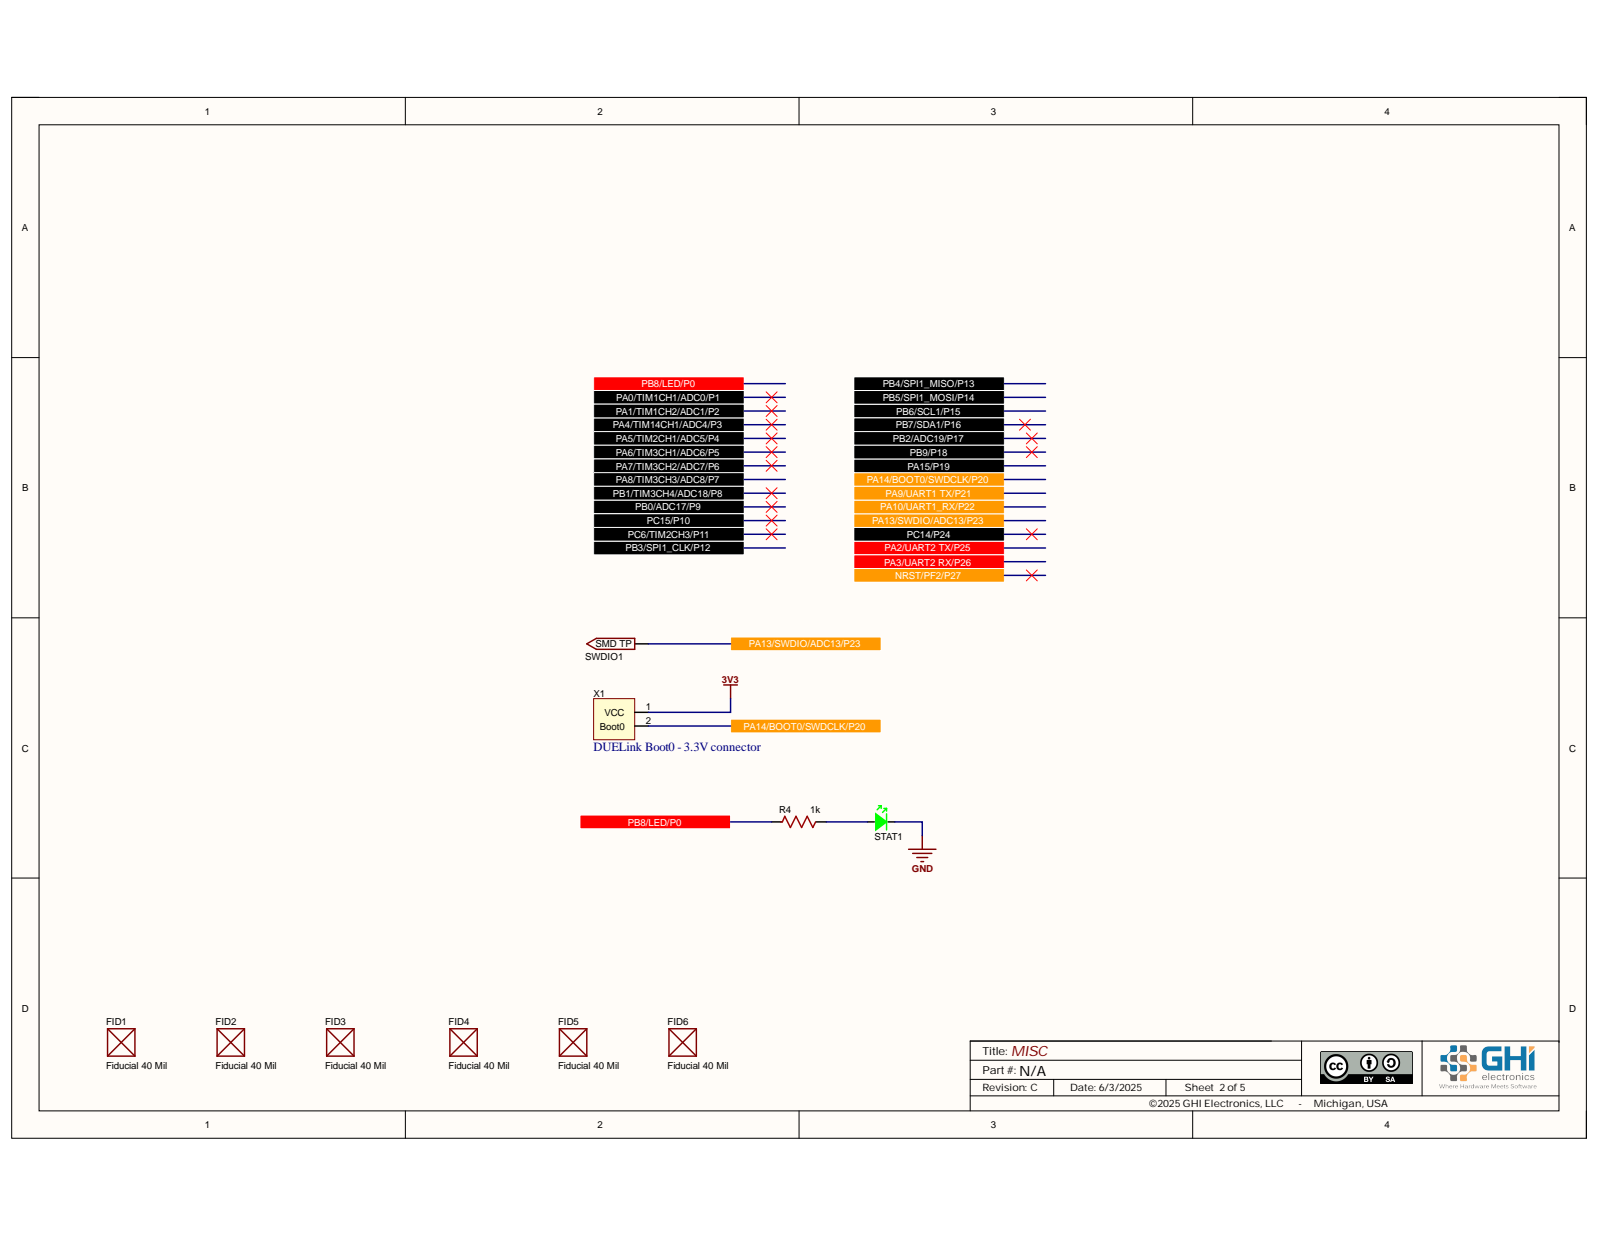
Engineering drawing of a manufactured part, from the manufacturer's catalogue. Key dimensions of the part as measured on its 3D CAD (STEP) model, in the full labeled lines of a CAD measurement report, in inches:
Part name (STEP PRODUCT): PCB; Board; C1; C0402 (+7 more)
STEP written by: Open CASCADE 7.5 (AUTOMOTIVE_DESIGN)
Units: inches
Bodies: 189 solids, 4613 faces (2992 planar, 628 cylindrical, 993 other)
Overall size (bounding box): 1.457 × 1.144 × 0.956
Volume: 0.311 in³ · Surface area: 15.88 in²
Round holes (diameter × count): ⌀0.04 ×12, ⌀0.118 ×4, ⌀0.04 ×2
Partial cylindrical surfaces — rounded edges, fillets, slot ends (radius × count): R0.005 ×35, R0.006 ×14, R0.138 ×4, R0.007 ×2, R0.007 ×2, R0.007 ×2
Main face-to-face distances: 0.205, 0.197, 0.791, 0.799, 0.594, 0.614, 0.272, 0.264, 0.067, 0.528
Hole centre spacings: 0.806, 0.8, 0.854, 0.1, 0.1, 0.2, 0.2, 0.3
